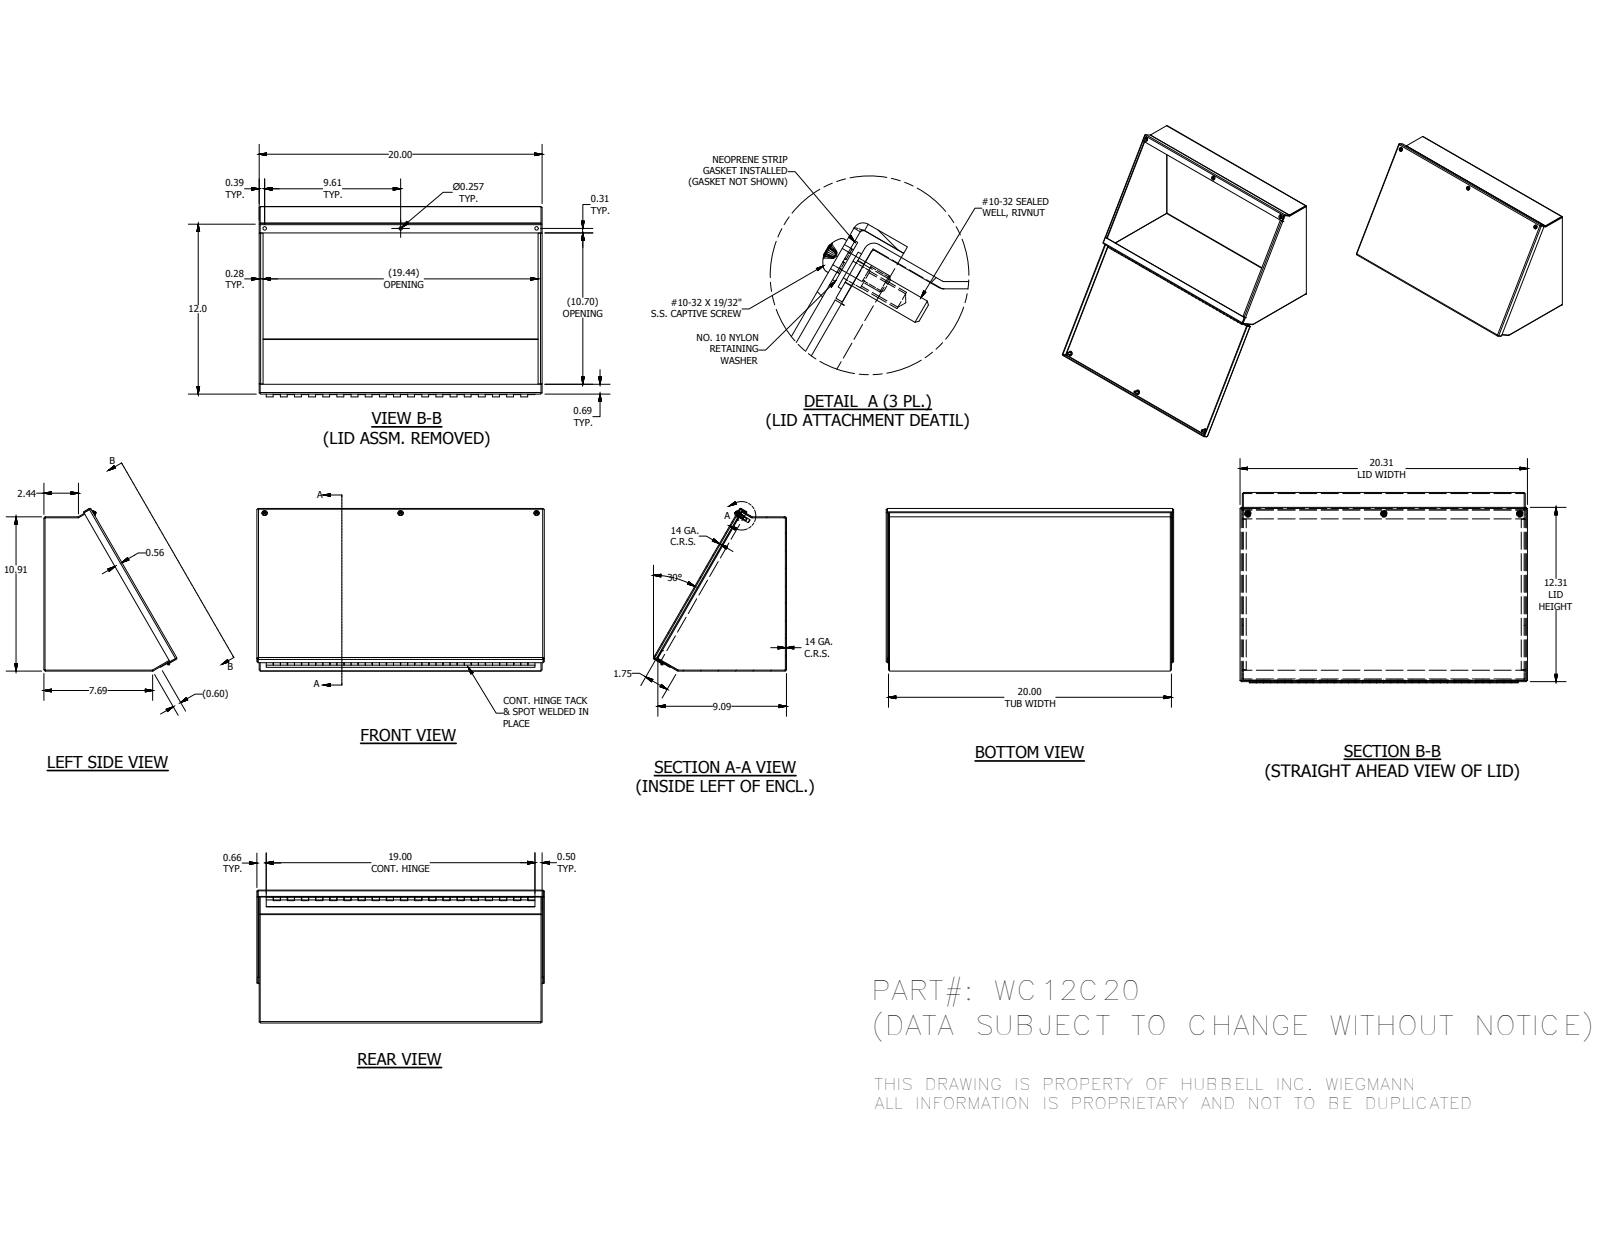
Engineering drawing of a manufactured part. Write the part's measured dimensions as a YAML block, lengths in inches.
part_name: "WC12C20BTB; WC12C20LID; WC12CLS; WC12CRS (+8 more)"
step_written_by: "Autodesk Inventor 2014 (AUTOMOTIVE_DESIGN)"
units: inches
bodies: {solids: 16, faces: 557, planar: 340, cylindrical: 143, other: 74}
overall_size: [20.313, 11.499, 9.395]
volume: 68.83
surface_area: 1910
round_holes:
  - {diameter: 0.156, count: 3}
  - {diameter: 0.196, count: 3}
  - {diameter: 0.257, count: 3}
  - {diameter: 0.278, count: 3}
  - {diameter: 0.281, count: 3}
  - {diameter: 0.117, count: 1}
round_bosses_or_shafts:
  - {diameter: 0.453, count: 3}
  - {diameter: 0.406, count: 3}
  - {diameter: 0.373, count: 3}
  - {diameter: 0.248, count: 3}
  - {diameter: 0.19, count: 3}
  - {diameter: 0.2, count: 1}
  - {diameter: 0.1, count: 1}
partial_cylinders:
  - {radius: 0.031, count: 12}
  - {radius: 0.105, count: 12}
  - {radius: 0.089, count: 3}
face_to_face_distances: [0.074, 19.926, 10.832, 19.852, 20, 10.758, 10.906, 0.116, 12, 0.042]
hole_center_spacings: [9.613, 19.226, 0.059]
